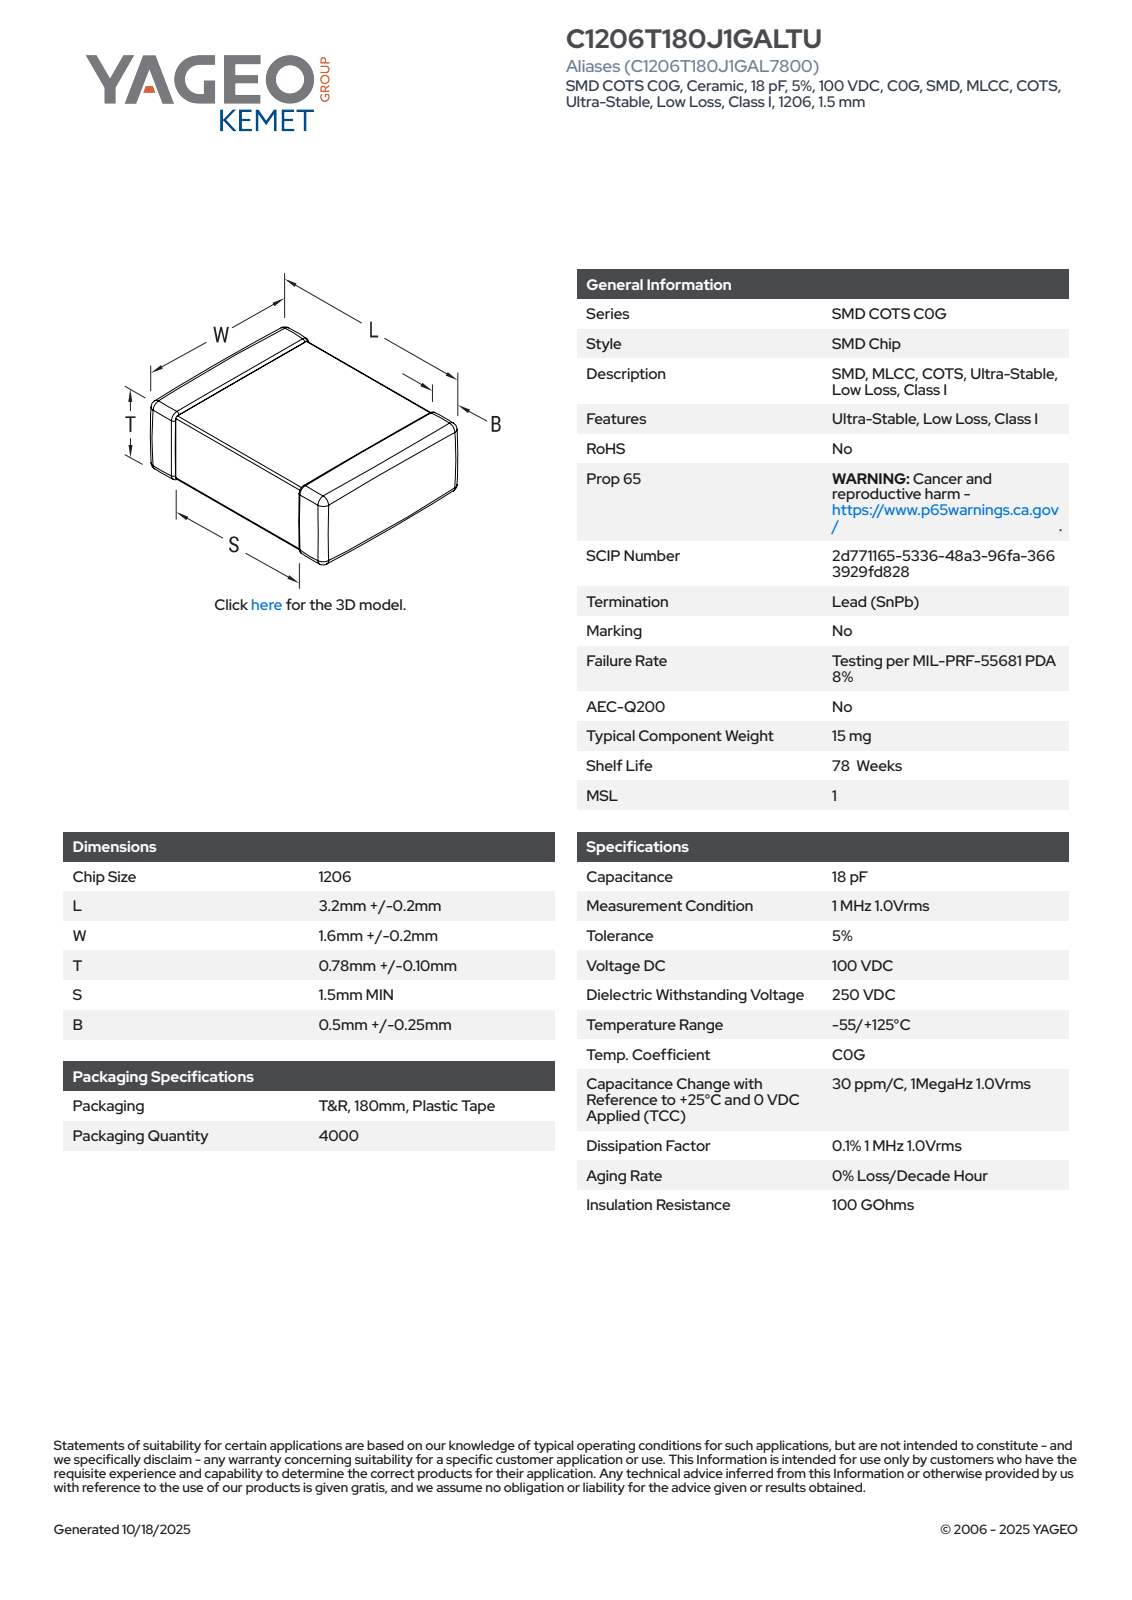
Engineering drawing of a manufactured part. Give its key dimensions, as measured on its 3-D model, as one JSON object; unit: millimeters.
{"part_name": "CCS_STDNOS_1206_L3.4W1.8T0.88B0.5", "step_written_by": "SolidWorks 2014 (AUTOMOTIVE_DESIGN)", "units": "millimeters", "bodies": {"solids": 4, "faces": 121, "planar": 71, "cylindrical": 34, "other": 16}, "overall_size": [3.4, 1.8, 0.88], "volume_mm3": 5, "surface_area_mm2": 21, "face_to_face_distances": [0.8, 0.84, 1.72, 0.88, 3.4, 1.76, 1.8, 0.85, 0.81, 0.72]}
